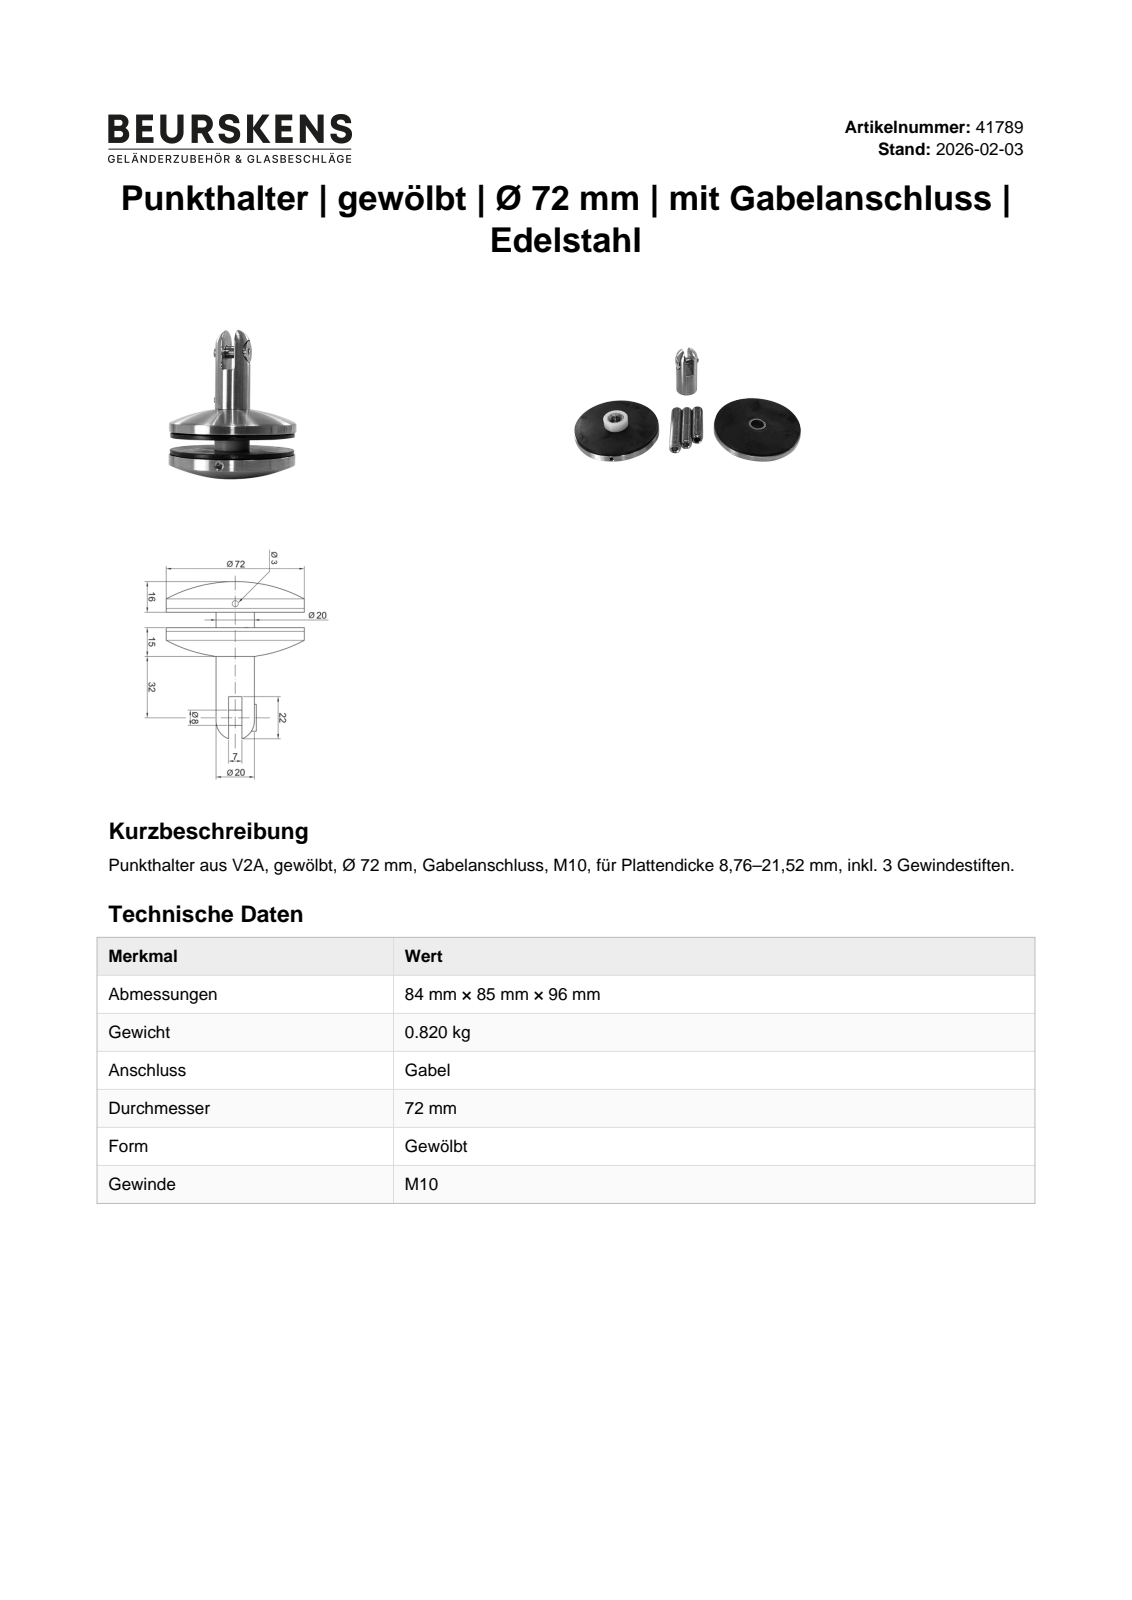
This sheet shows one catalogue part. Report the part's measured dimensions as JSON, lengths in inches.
{"part_name": "41789; Kopf 41735; 40903; 40910 Kunststoff weiß (+5 more)", "step_written_by": "Autodesk Inventor 2023 (AUTOMOTIVE_DESIGN)", "units": "inches", "bodies": {"solids": 9, "faces": 84, "planar": 46, "cylindrical": 23, "other": 15}, "overall_size": [3.367, 2.835, 2.835], "volume_in3": 6.703, "surface_area_in2": 68.29, "round_holes": [[0.118, 1], [0.197, 1], [0.315, 1], [0.335, 1], [0.394, 1], [0.492, 1], [0.551, 1], [0.559, 1]], "round_bosses_or_shafts": [[2.835, 1], [2.756, 1], [0.795, 1], [0.787, 1], [0.472, 1]], "face_to_face_distances": [0.079, 0.611, 0.69, 0.532, 0.531, 0.61, 1.143, 1.221, 0.276, 0.828], "hole_center_spacings": [1.063, 1.536, 2.599]}
